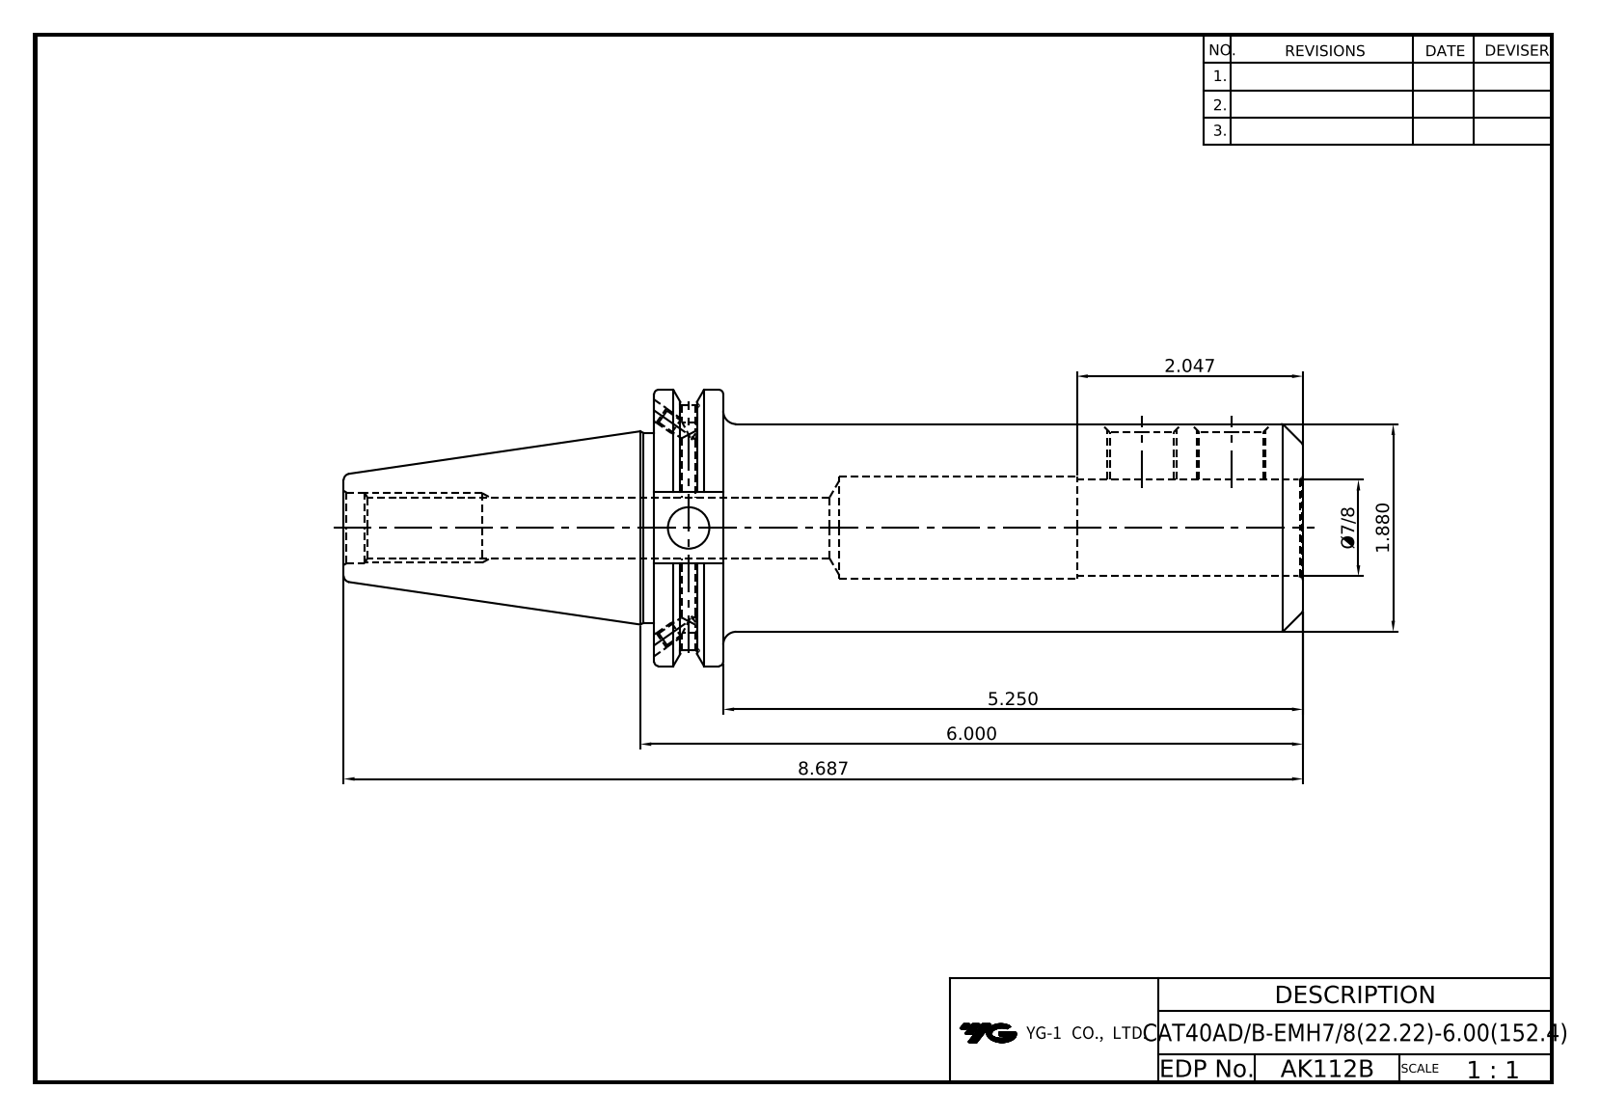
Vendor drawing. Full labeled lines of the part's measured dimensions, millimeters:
Part name (STEP PRODUCT): LO-CAT40ADB-EMH22.225-152.4
STEP written by: Autodesk Inventor 2025 (AUTOMOTIVE_DESIGN)
Units: millimetres
Bodies: 1 solid, 87 faces (37 planar, 29 cylindrical, 21 other)
Overall size (bounding box): 220.65 × 63.5 × 61.09
Volume: 289 836 mm³ · Surface area: 49 163 mm²
Round holes (diameter × count): ⌀3.24 ×4, ⌀4 ×2, ⌀4.2 ×2, ⌀9.53 ×1, ⌀13.39 ×1, ⌀16.3 ×1, ⌀22.23 ×1, ⌀23.43 ×1
Round bosses / shafts (diameter × count): ⌀63.5 ×1, ⌀47.75 ×1, ⌀43.6 ×1
Partial cylindrical surfaces — rounded edges, fillets, slot ends (radius × count): R8.19 ×1, R28.15 ×1
Main face-to-face distances: 149.23, 15.88, 133.35, 42.55, 26.67, 106.68, 47.6, 16.38, 71.42, 87.3
